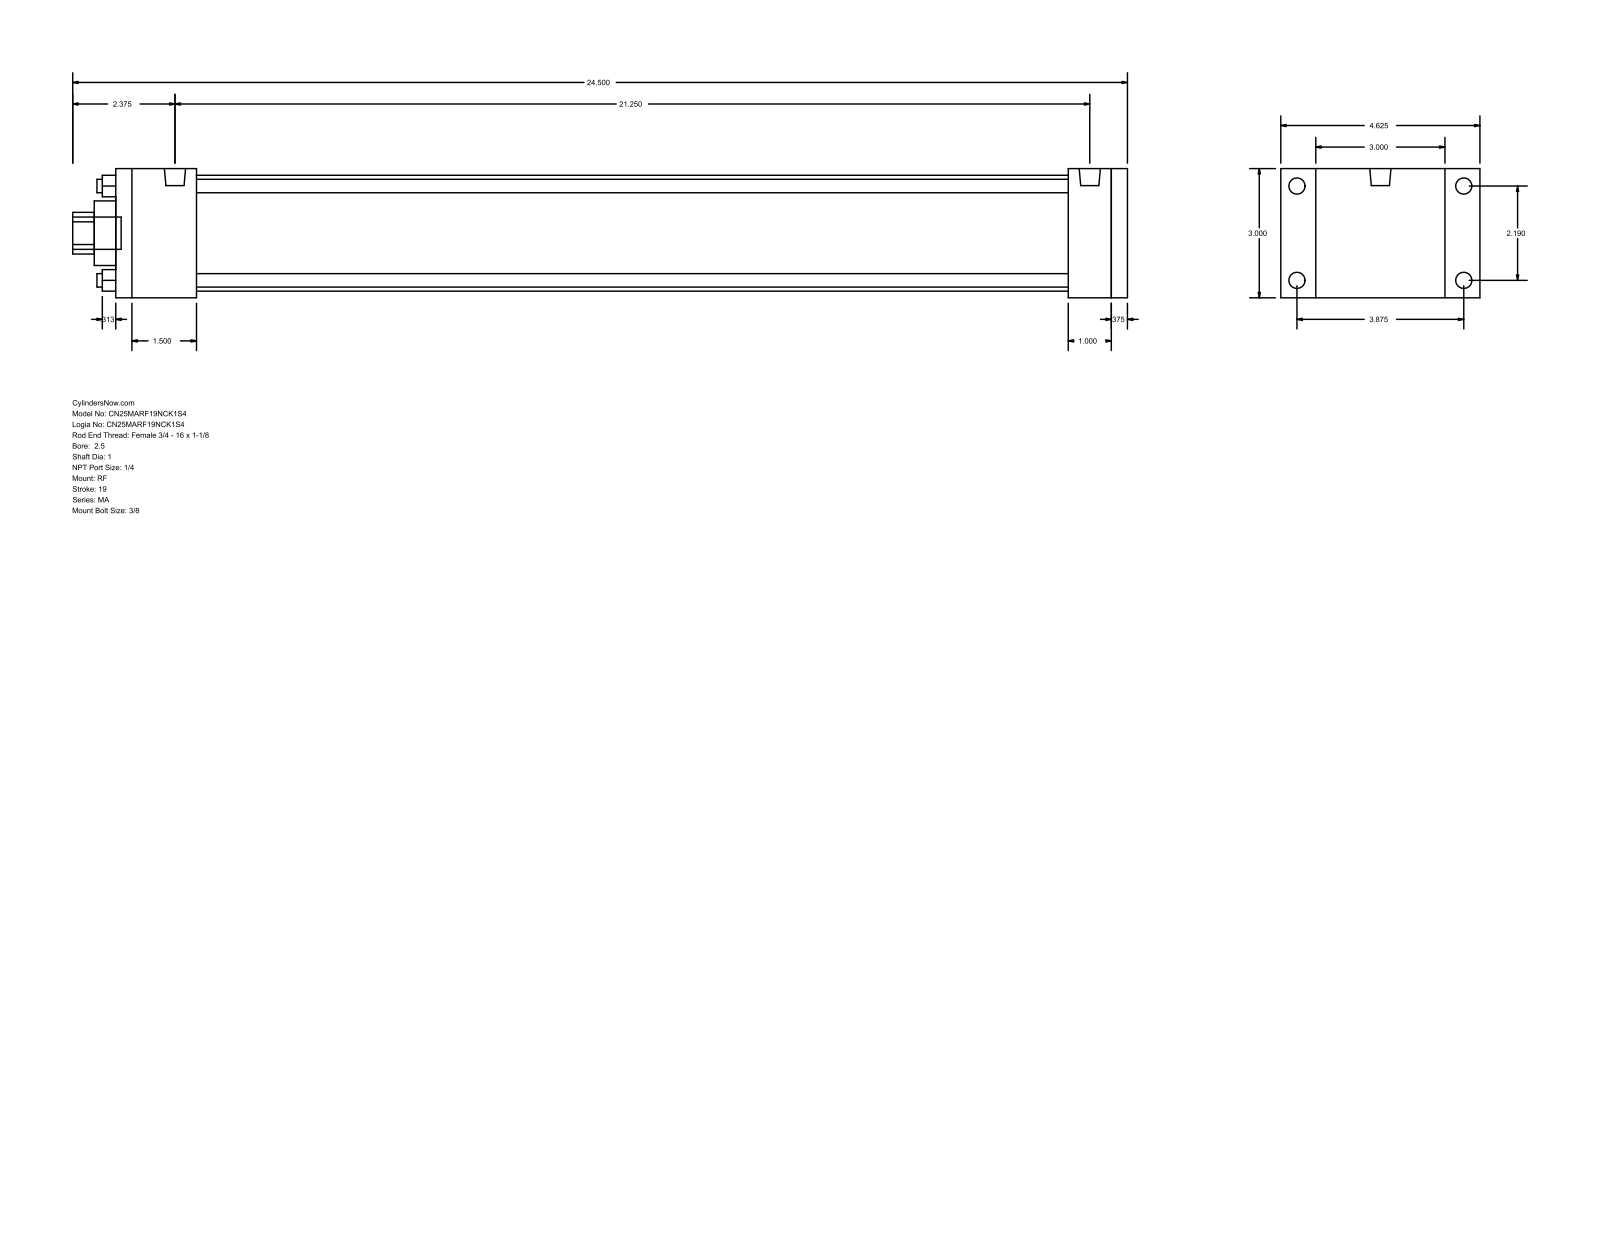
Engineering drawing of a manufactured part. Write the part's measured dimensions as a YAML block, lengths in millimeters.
part_name: "MA_RF__0250_1"
step_written_by: "GSSL Pune (CONFIG_CONTROL_DESIGN)"
units: millimeters
bodies: {solids: 0, faces: 92, planar: 64, cylindrical: 28, other: 0}
overall_size: [622.3, 117.47, 76.2]
round_holes:
  - {diameter: 7.94, count: 4}
  - {diameter: 25.4, count: 1}
  - {diameter: 38.1, count: 1}
  - {diameter: 68.33, count: 1}
round_bosses_or_shafts:
  - {diameter: 9.53, count: 4}
  - {diameter: 7.94, count: 4}
  - {diameter: 12.49, count: 2}
  - {diameter: 19.05, count: 1}
partial_cylinders:
  - {radius: 12.29, count: 1}
face_to_face_distances: [76.2, 596.9, 9.53, 587.37, 47.63, 561.98, 514.35, 539.74, 549.27, 25.39]
hole_center_spacings: [39.33, 55.62, 78.66]
